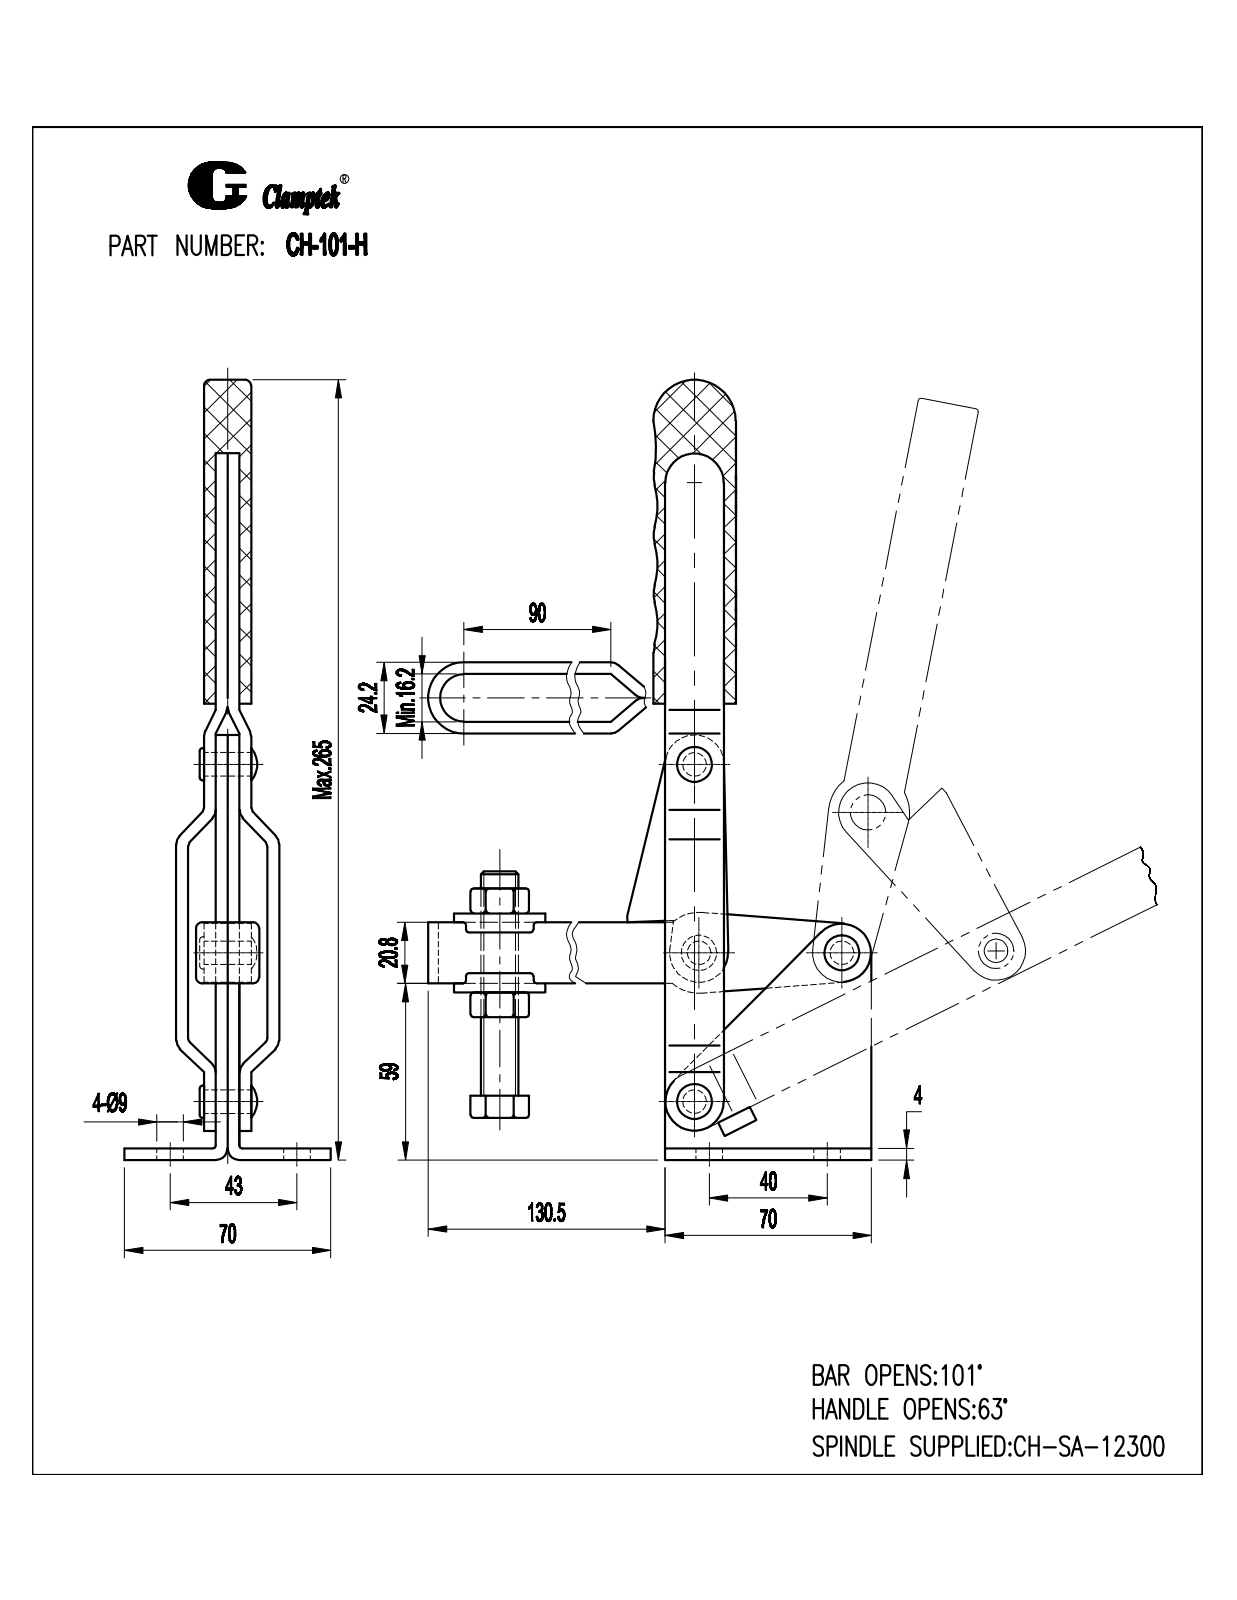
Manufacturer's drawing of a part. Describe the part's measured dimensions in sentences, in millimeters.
The part is named "CH-101-H-01 FLANGED BASE; CH-SA-12300 SPINDLE SUPPLIED; CH-SA-12300 Nut; CH-101-H (+6 more)". Its 3-D file was written by "SolidWorks 2010 (CONFIG_CONTROL_DESIGN)". It is 17 solids with 1571 faces: 635 planar, 455 cylindrical and 481 other. Overall it measures 270.46 by 200 by 70 millimeters. Its volume is 182 221 cubic millimeters and its surface area 111 140 square millimeters. Round holes: 4 of diameter 8, 4 of diameter 9, 1 of diameter 4, 1 of diameter 10.5, 1 of diameter 13. Round bosses or shafts: 1 of diameter 12.7, 1 of diameter 3.6. Partial cylindrical surfaces (rounded edges, fillets, slot ends): 84 of radius 0.25, 26 of radius 4, 8 of radius 1, 8 of radius 10, 8 of radius 25.91, 7 of radius 3, 7 of radius 3.5, 4 of radius 2. The main face-to-face distances are 4, 8, 4.25, 8.25, 20.5, 12.25, 16.25, 16.5, 24.75, 8.5. The hole center spacings are 40, 43, 58.73, 116.99, 156.48, 48.5, 50.89, 64.
